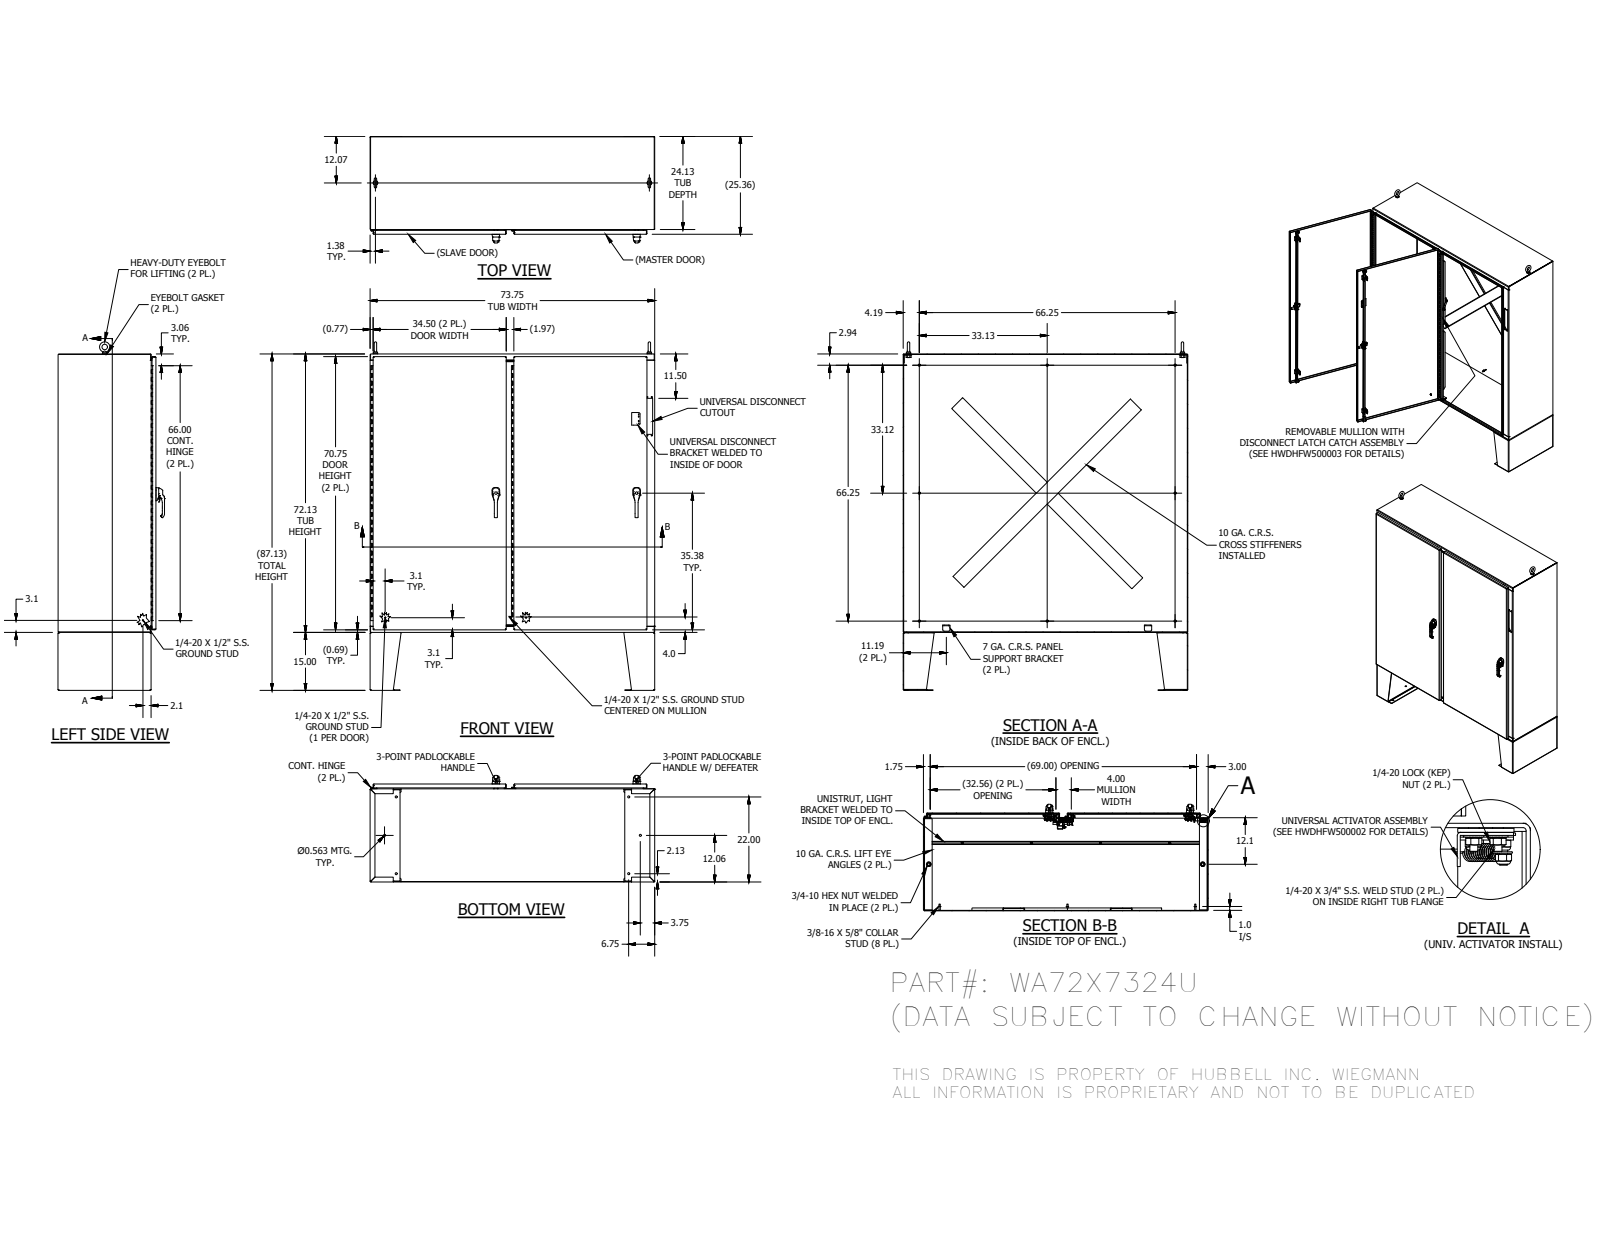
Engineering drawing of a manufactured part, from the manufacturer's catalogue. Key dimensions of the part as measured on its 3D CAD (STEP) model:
Part name (STEP PRODUCT): WA72X7324UBLS; WAX7324UTOP; WAX7324UBTM; HFW332010S (+8 more)
STEP written by: Autodesk Inventor 2016 (AUTOMOTIVE_DESIGN)
Units: millimetres
Bodies: 216 solids, 8897 faces (4142 planar, 2994 cylindrical, 1761 other)
Overall size (bounding box): 2292.29 × 1873.25 × 701.25
Volume: 48 460 000 mm³ · Surface area: 29 490 000 mm²
Round holes (diameter × count): ⌀6.35 ×18, ⌀9.52 ×18, ⌀14.29 ×18, ⌀4.83 ×8, ⌀5.08 ×8, ⌀5.16 ×8, ⌀7.02 ×8, ⌀7.33 ×8, ⌀7.94 ×8, ⌀8.51 ×8, ⌀9.65 ×8, ⌀5.11 ×7
Round bosses / shafts (diameter × count): ⌀6.35 ×22, ⌀8.38 ×18, ⌀15.88 ×13, ⌀8.56 ×12, ⌀9.52 ×11, ⌀14.29 ×9, ⌀25.4 ×8, ⌀11.13 ×8
Partial cylindrical surfaces — rounded edges, fillets, slot ends (radius × count): R0.5 ×335, R0.3 ×203, R0.51 ×192, R0.47 ×42, R2.38 ×41, R1.27 ×40, R3.17 ×37, R2 ×27
Main face-to-face distances: 3.4, 640.5, 3.41, 637.1, 643.9, 1828.57, 1873.25, 1869.84, 1825.16, 1866.44
Hole centre spacings: 927.1, 0.93, 50.8, 927.37, 0.92, 22.5, 27.99, 29
